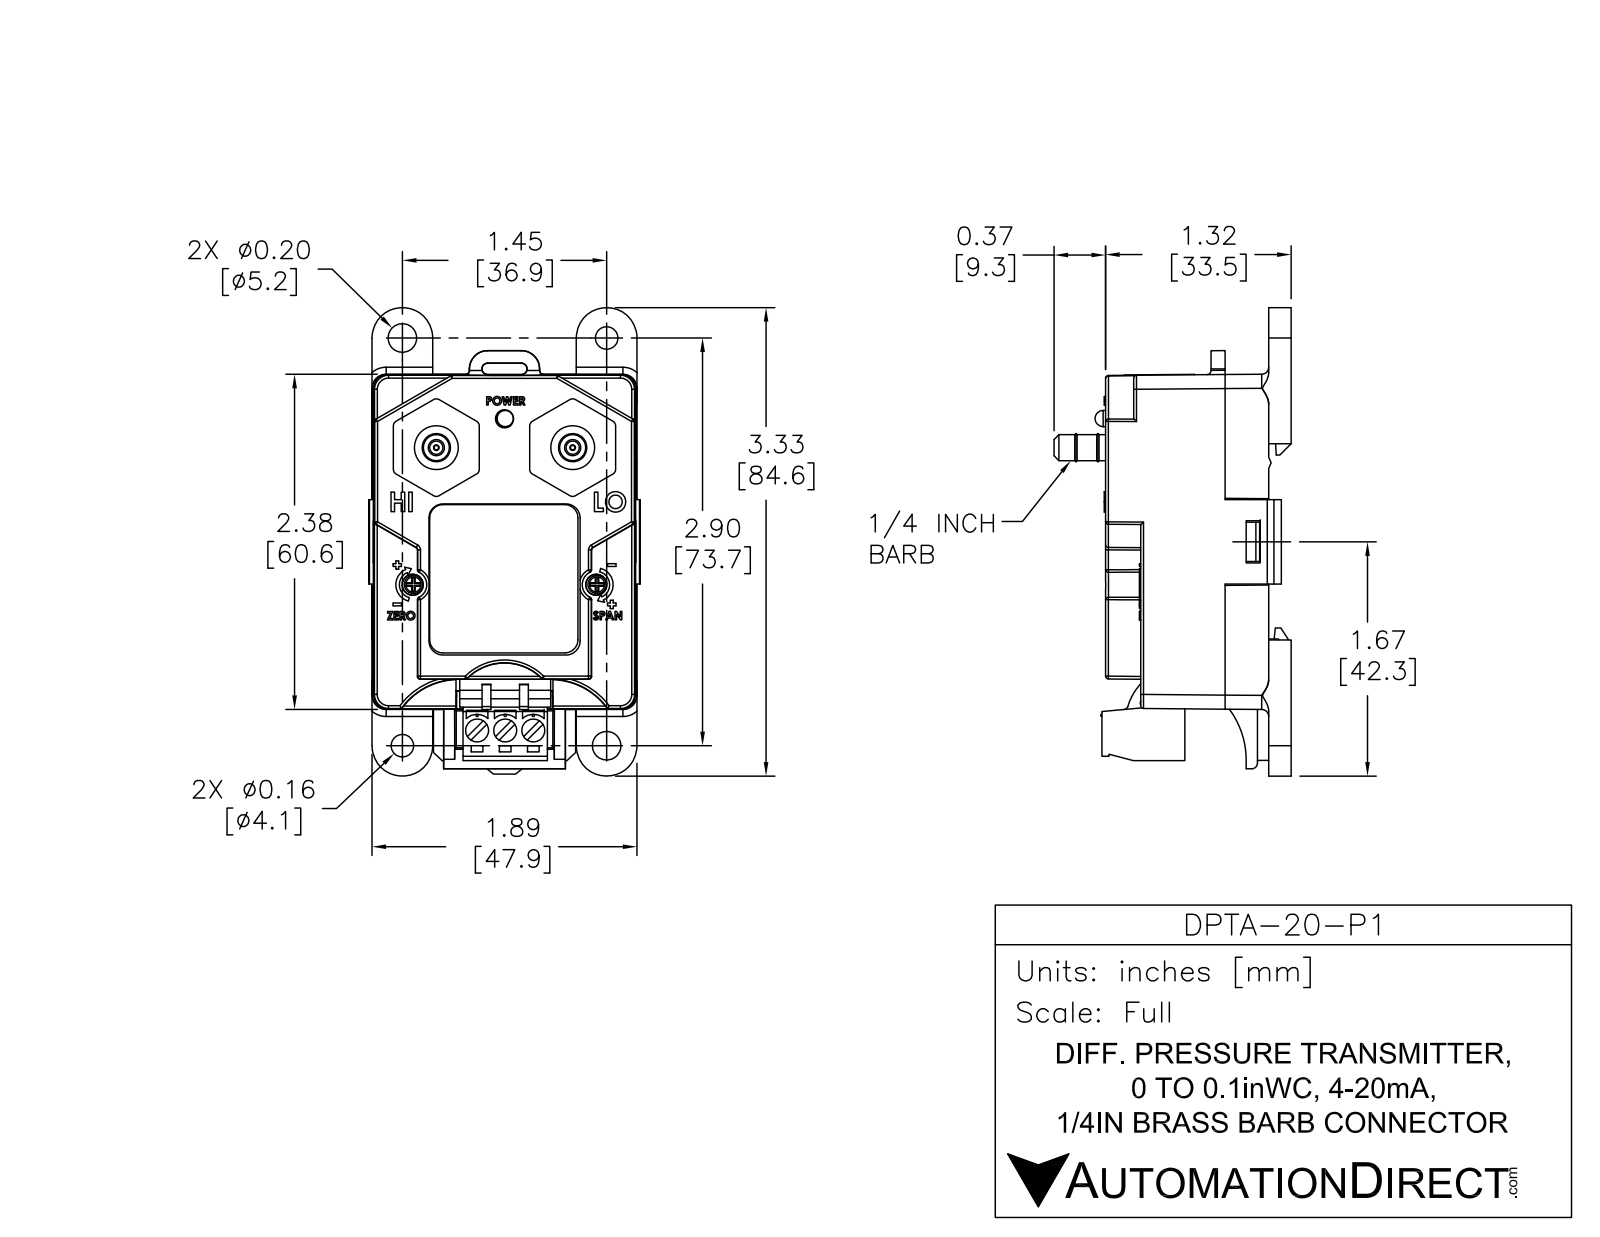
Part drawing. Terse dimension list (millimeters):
name: DPTA-20-P1
written by: SolidWorks 2011 (AUTOMOTIVE_DESIGN)
unit: mm
bodies: 11 solids, 448 faces (354 planar, 85 cylindrical, 9 other)
size: 85.01 × 49.76 × 43.1
volume: 29 684 mm³; area: 34 743 mm²
holes: 7× ⌀4, 2× ⌀2.5, 2× ⌀5.12, 1× ⌀3.1
bosses: 3× ⌀5, 3× ⌀3.5, 3× ⌀3.5, 2× ⌀8, 2× ⌀4.75, 1× ⌀3
rounds: 12× R3, 4× R2, 4× R5.5, 2× R0.99, 2× R1.06, 2× R1.12, 2× R2.38, 2× R3.25
face distances: 1, 1.9, 4, 29.1, 0.5, 46.9, 5.9, 5, 33.1, 27.2
hole spacings: 13.55, 20.73, 23.37, 24.92, 29.43, 34.46, 36.67, 38.22
